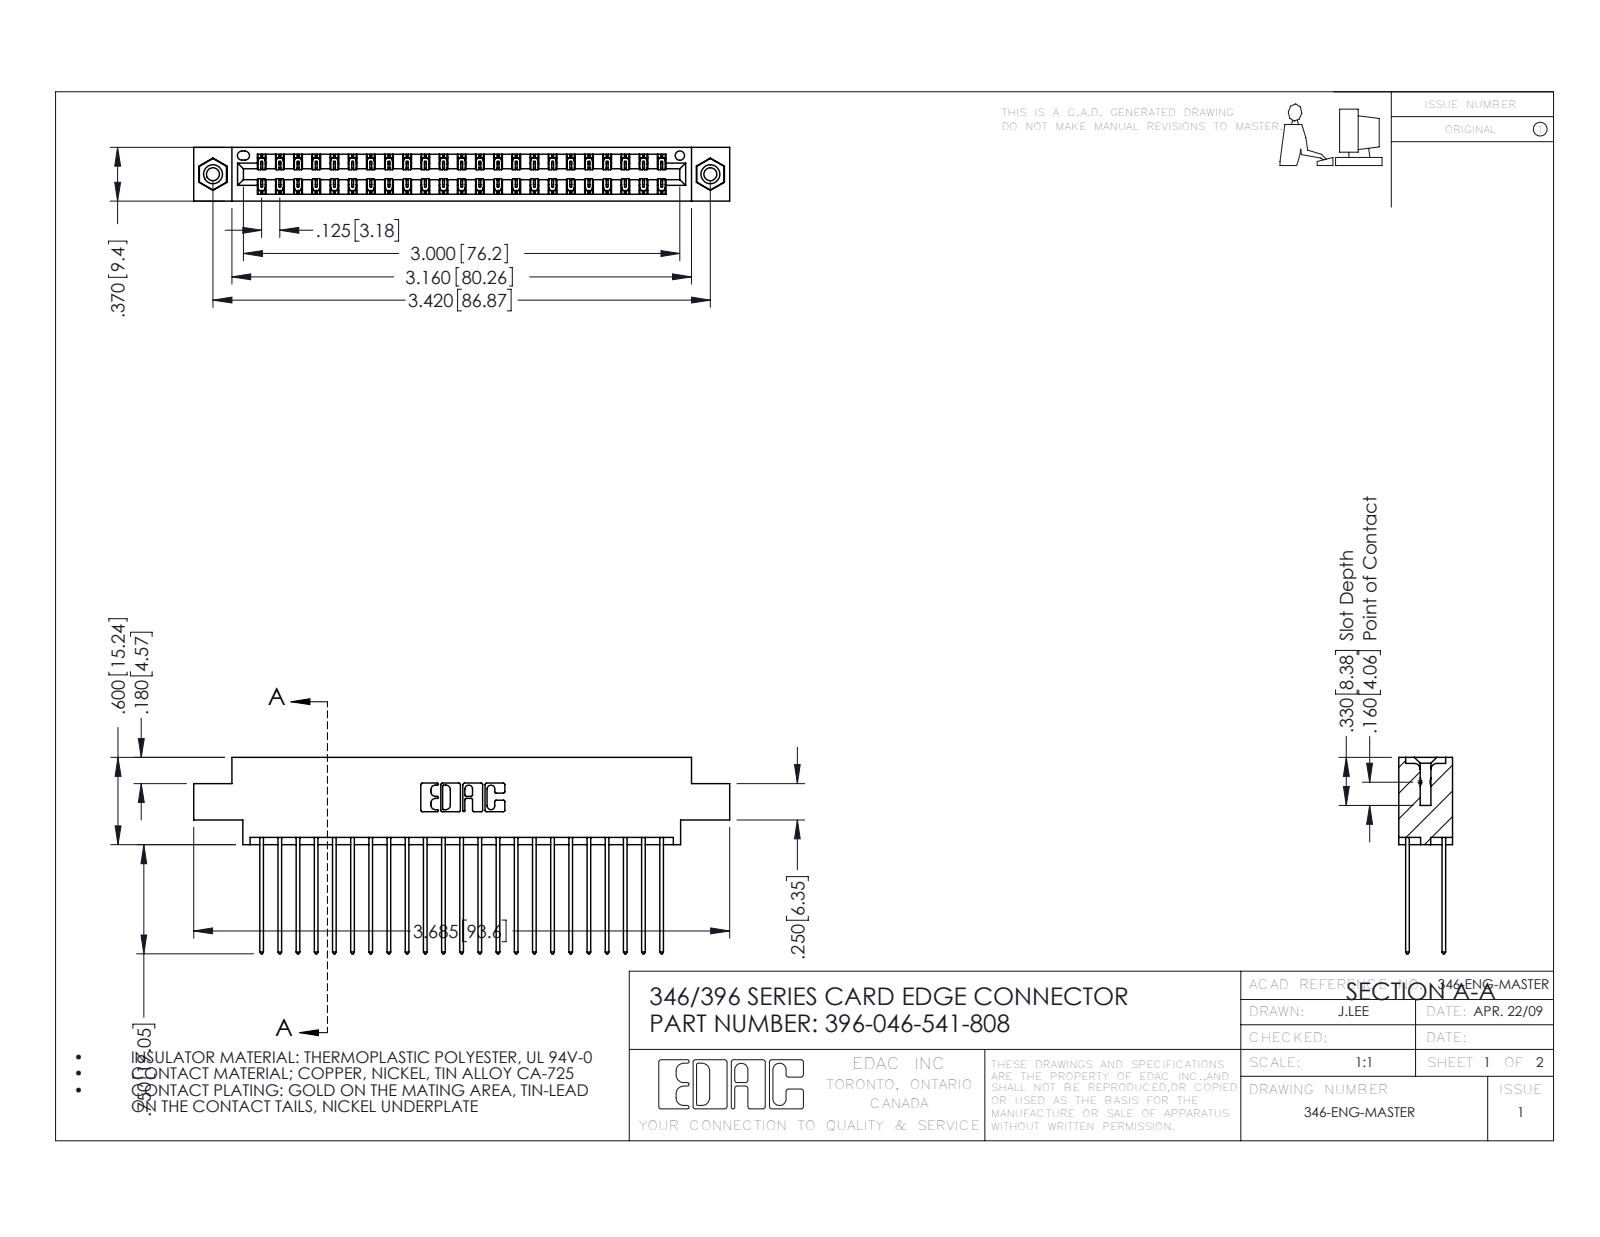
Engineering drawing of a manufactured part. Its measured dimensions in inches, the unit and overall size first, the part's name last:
Units: inches
Overall size (bounding box): 3.685 × 1.35 × 0.37
Round holes (diameter × count): ⌀0.089 ×2, ⌀0.125 ×2, ⌀0.156 ×2, ⌀0.064 ×1
Round bosses / shafts (diameter × count): ⌀0.155 ×2
Partial cylindrical surfaces — rounded edges, fillets, slot ends (radius × count): R0.006 ×69, R0.01 ×46, R0.01 ×22, R0.007 ×6, R0.031 ×6, R0.026 ×3, R0.014 ×2, R0.022 ×2
Main face-to-face distances: 0.048, 0.322, 0.25, 0.072, 0.298, 0.025, 0.37, 0.275, 0.225, 0.222
Hole centre spacings: 0.246, 3.212, 3.42
Volume: 0.554 in³ · Surface area: 21.16 in²
Bodies: 49 solids, 2578 faces (1722 planar, 840 cylindrical, 16 other)
Part name (STEP PRODUCT): 345-292-001_345-293-141; 345-250-001_345-250-003-102; 396-046-541-808; 346 Part_0.170 Offset - 0.156 Dia-TI
STEP written by: SolidWorks 2016 (CONFIG_CONTROL_DESIGN)
